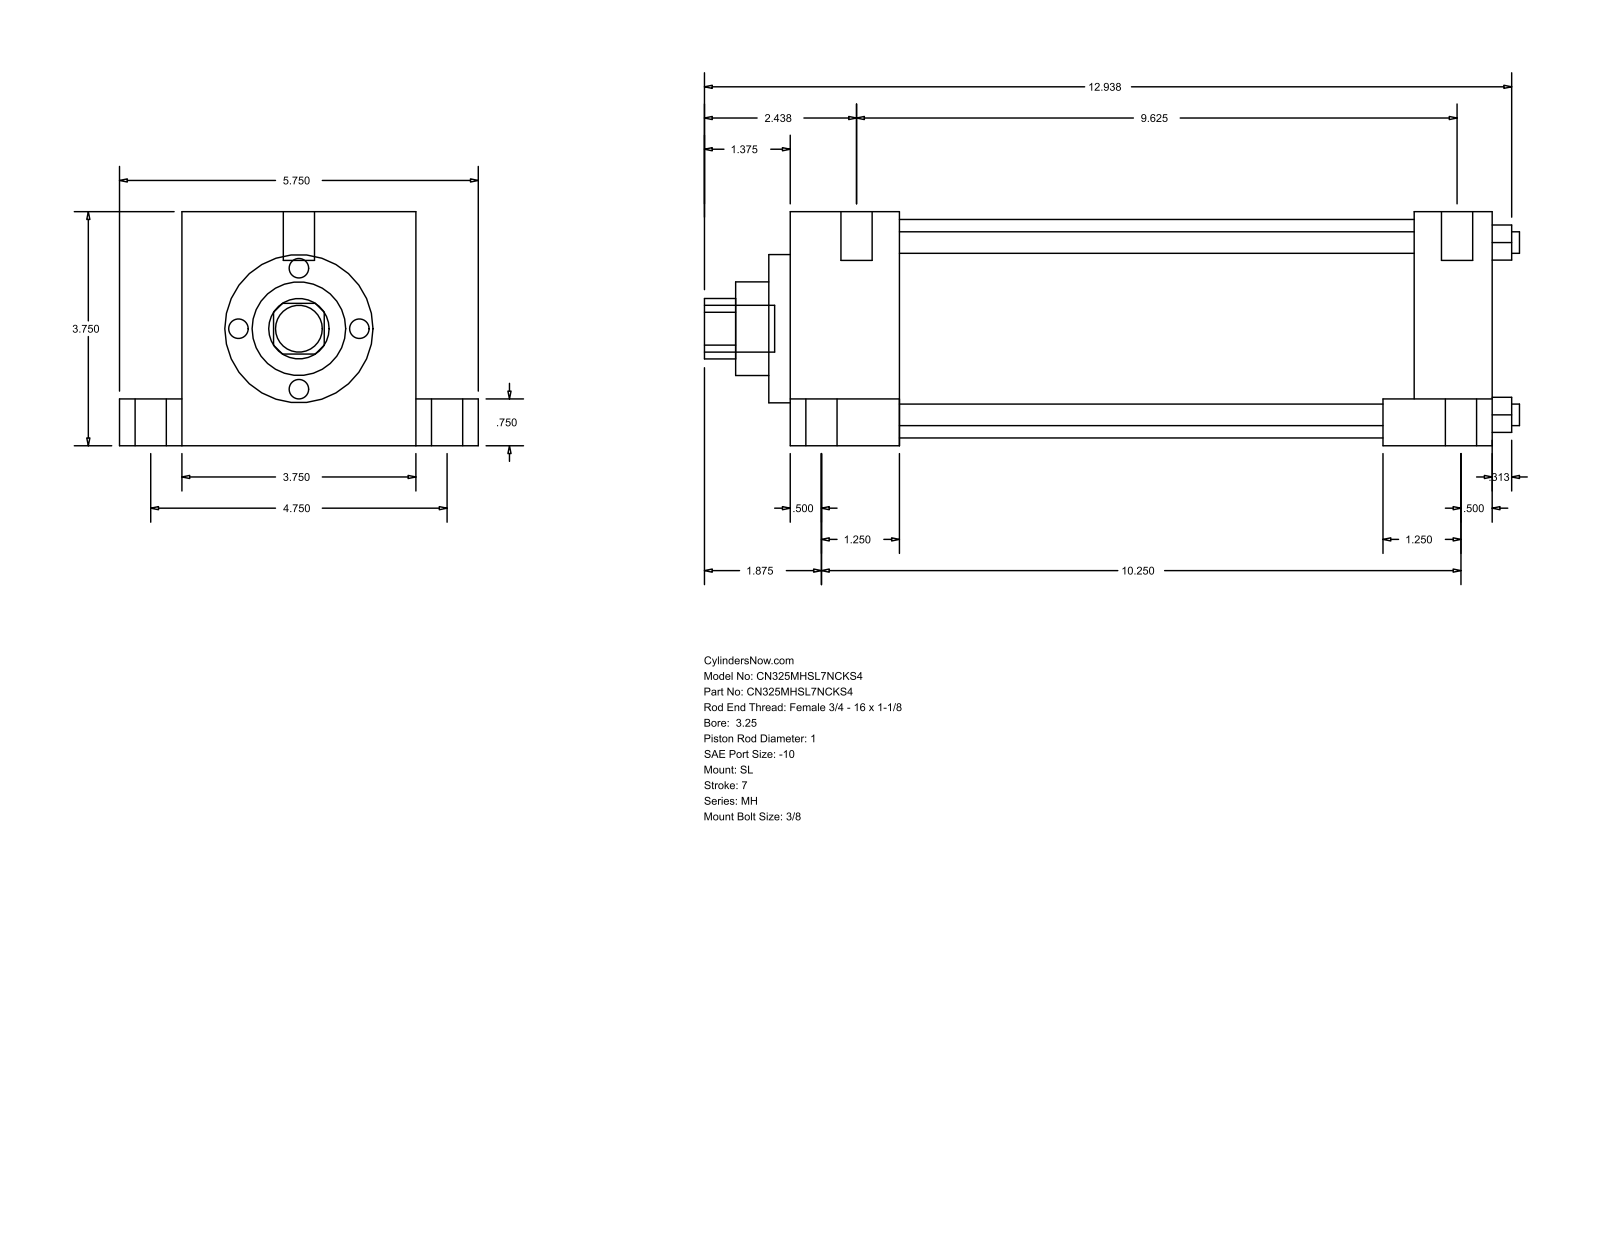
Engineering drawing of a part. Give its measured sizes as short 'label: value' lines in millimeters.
name: MH_SL__0325_1
written by: GSSL Pune (CONFIG_CONTROL_DESIGN)
unit: mm
bodies: 0 solids, 110 faces (77 planar, 33 cylindrical, 0 other)
size: 331.79 × 146.05 × 95.25
holes: 4× ⌀8.76, 1× ⌀25.4, 1× ⌀38.1, 1× ⌀60.33, 1× ⌀88.9
bosses: 6× ⌀12.7, 5× ⌀19.05, 4× ⌀5.56
rounds: 1× R12.29
face distances: 95.24, 285.76, 44.46, 241.3, 25.41, 120.65, 19.05, 76.19, 254.01, 209.55
hole spacings: 49.57, 70.1, 99.14
